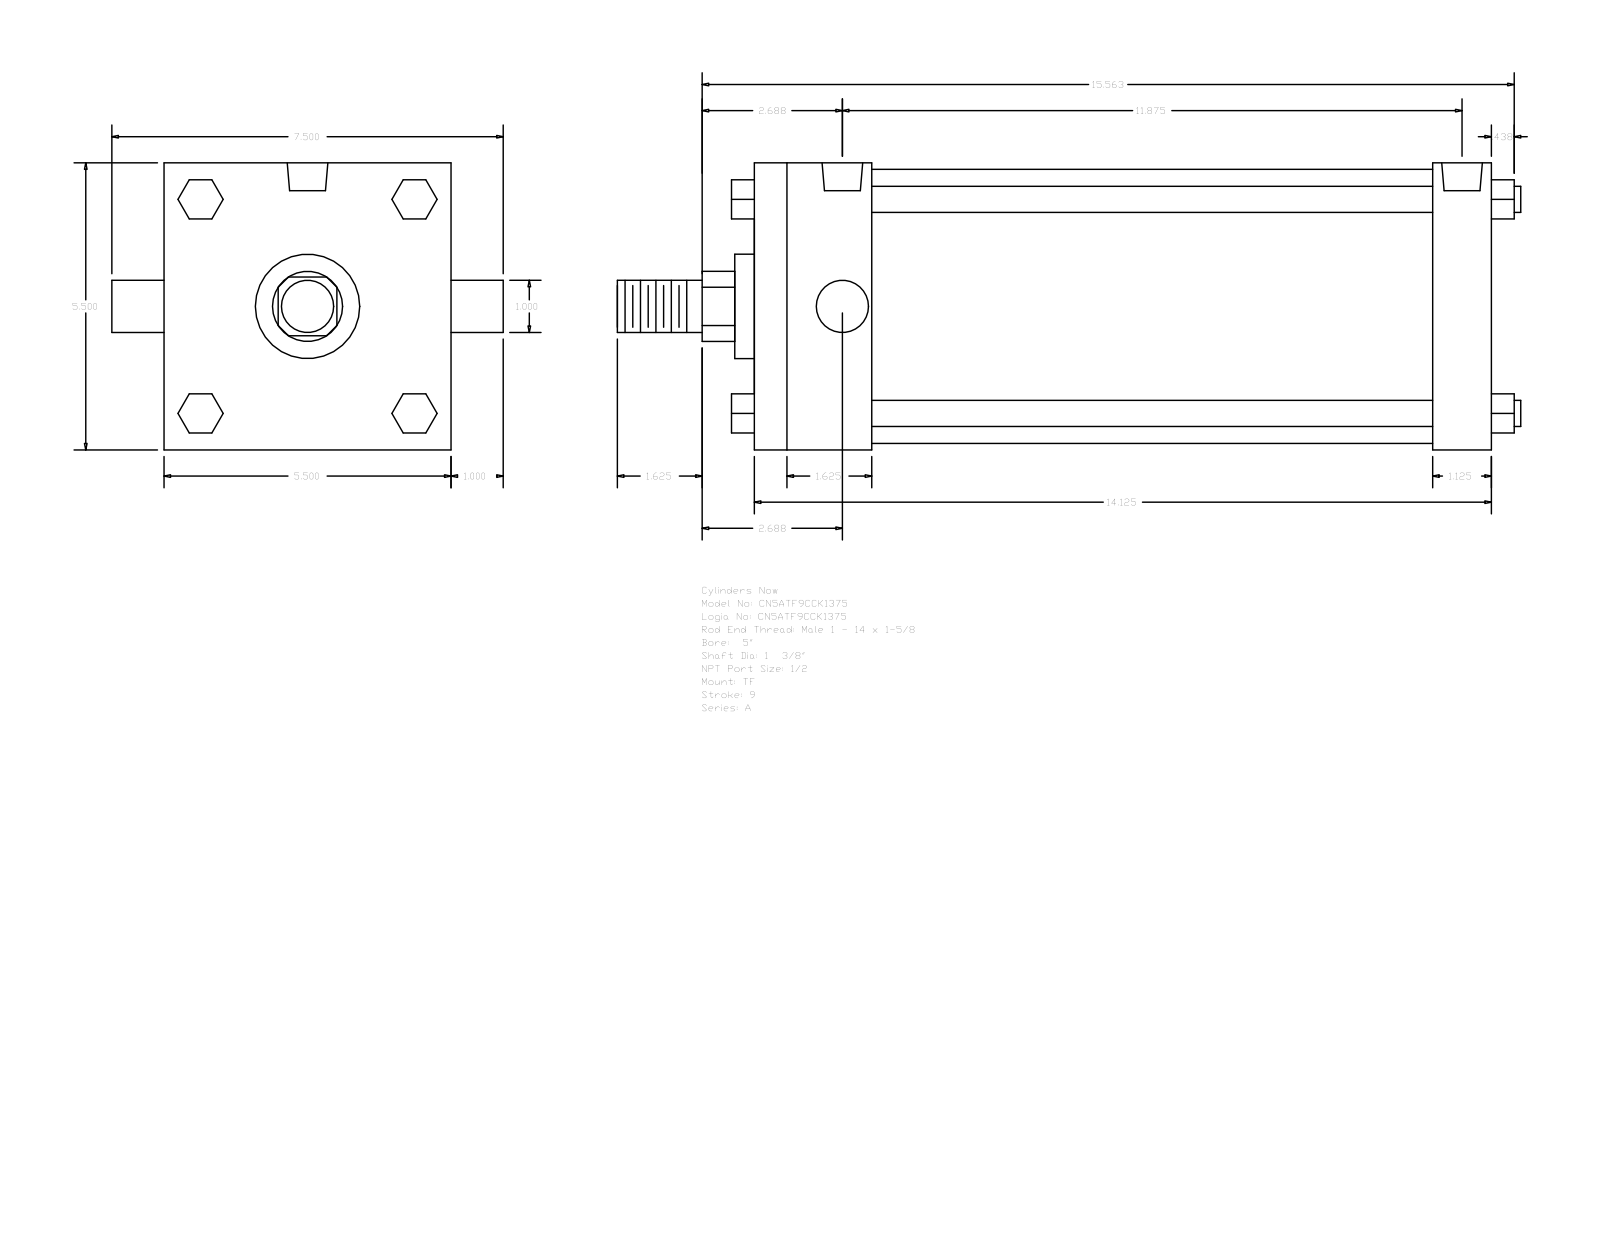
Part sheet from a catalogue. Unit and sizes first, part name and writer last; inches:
Units: inches
Overall size (bounding box): 17.313 × 7.5 × 5.5
Round holes (diameter × count): ⌀0.344 ×3, ⌀0.778 ×2
Round bosses / shafts (diameter × count): ⌀0.5 ×4, ⌀1 ×2, ⌀5.25 ×1, ⌀2 ×1, ⌀1.375 ×1
Partial cylindrical surfaces — rounded edges, fillets, slot ends (radius × count): R0.672 ×1
Main face-to-face distances: 5.5, 14.125, 2.25, 1.125, 13, 10.75, 11.875, 0.75, 2.05, 3.55
Hole centre spacings: 0.094, 11.781, 11.687, 11.875
Bodies: 0 solids, 120 faces (92 planar, 28 cylindrical, 0 other)
Part name (STEP PRODUCT): A_TF__0500_1.375
STEP written by: GSSL Pune (CONFIG_CONTROL_DESIGN)
